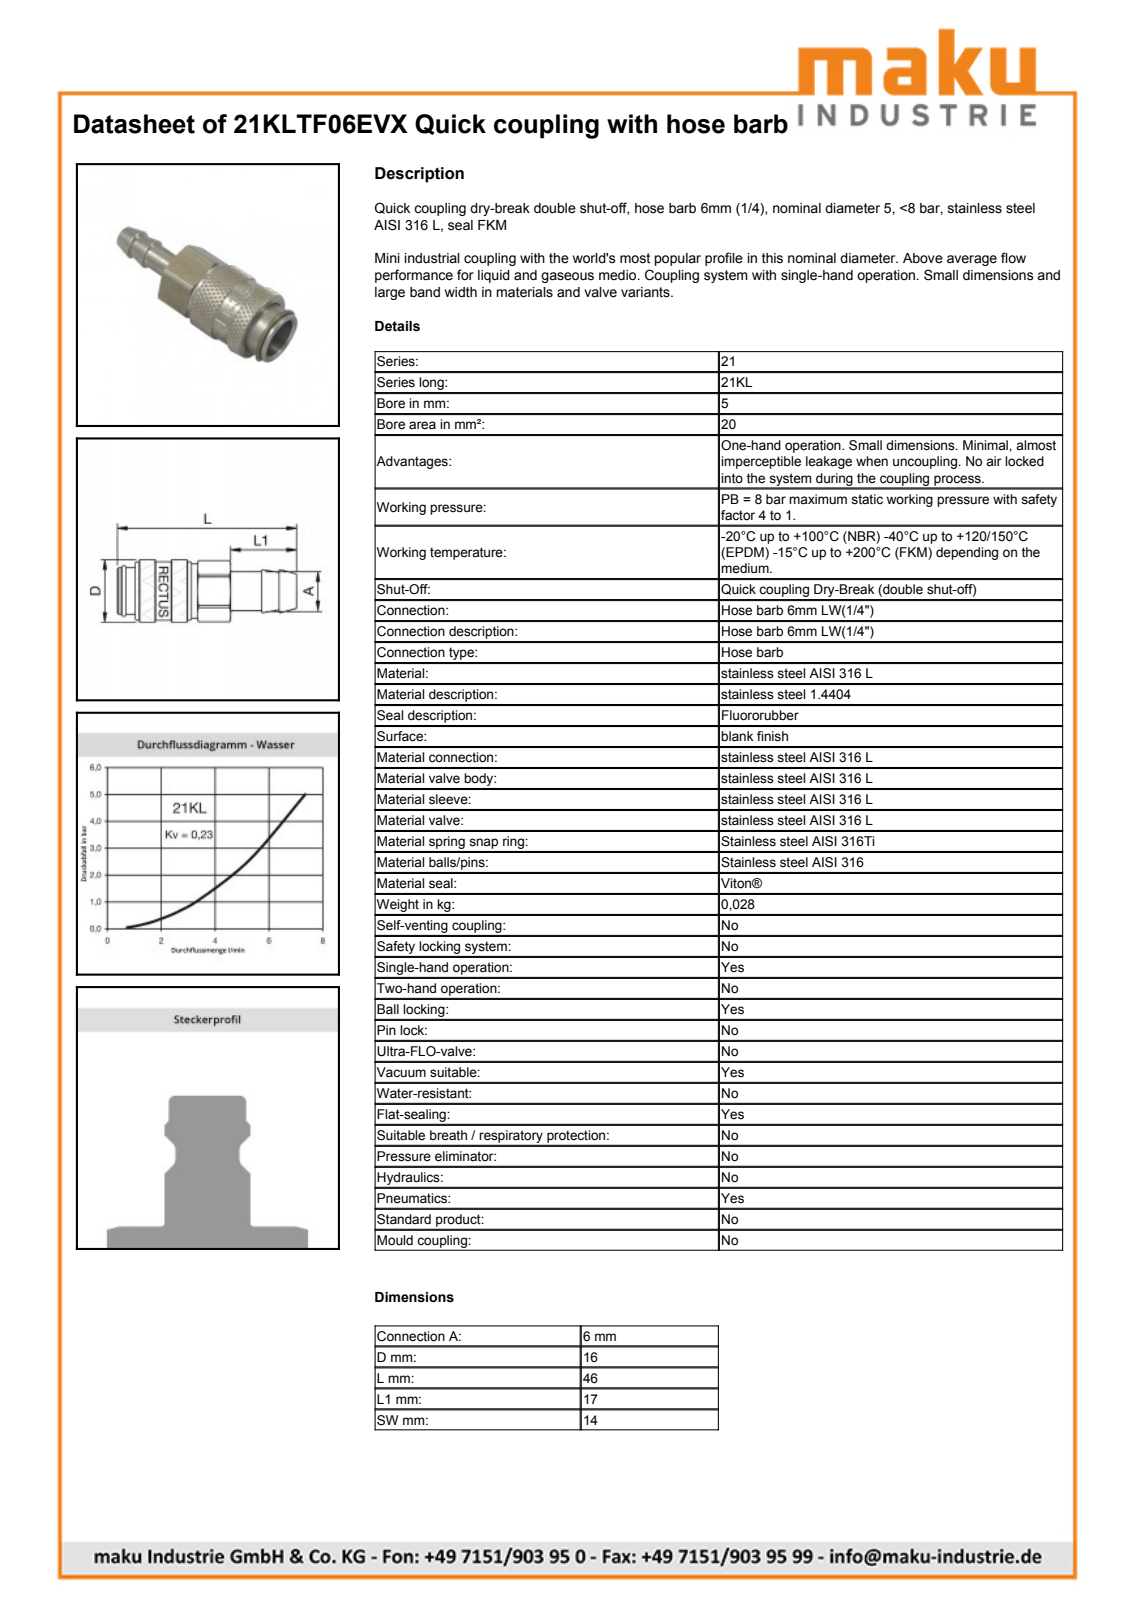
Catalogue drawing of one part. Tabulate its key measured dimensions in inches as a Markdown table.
| quantity | value |
| --- | --- |
| part name | D110824 |
| STEP written by | Autodesk Inventor 2013 (AUTOMOTIVE_DESIGN) |
| units | inches |
| bodies | 1 solid, 786 faces (296 planar, 93 cylindrical, 397 other) |
| overall size | 1.817 × 0.636 × 0.636 |
| volume | 0.317 in³ |
| surface area | 5.479 in² |
| round holes (diameter × count) | 0.478 × 1, 0.551 × 1 |
| round bosses / shafts (diameter × count) | 0.636 × 1, 0.594 × 1, 0.472 × 1, 0.449 × 1, 0.439 × 1, 0.422 × 1, 0.238 × 1 |
| partial cylindrical surfaces (radius × count) | 0.232 × 1, 0.293 × 1, 0.311 × 1 |
| main face-to-face distances | 0.551, 1.148, 0.636, 0.512, 0.177, 0.459, 0.971, 0.464, 0.287, 0.172 |
